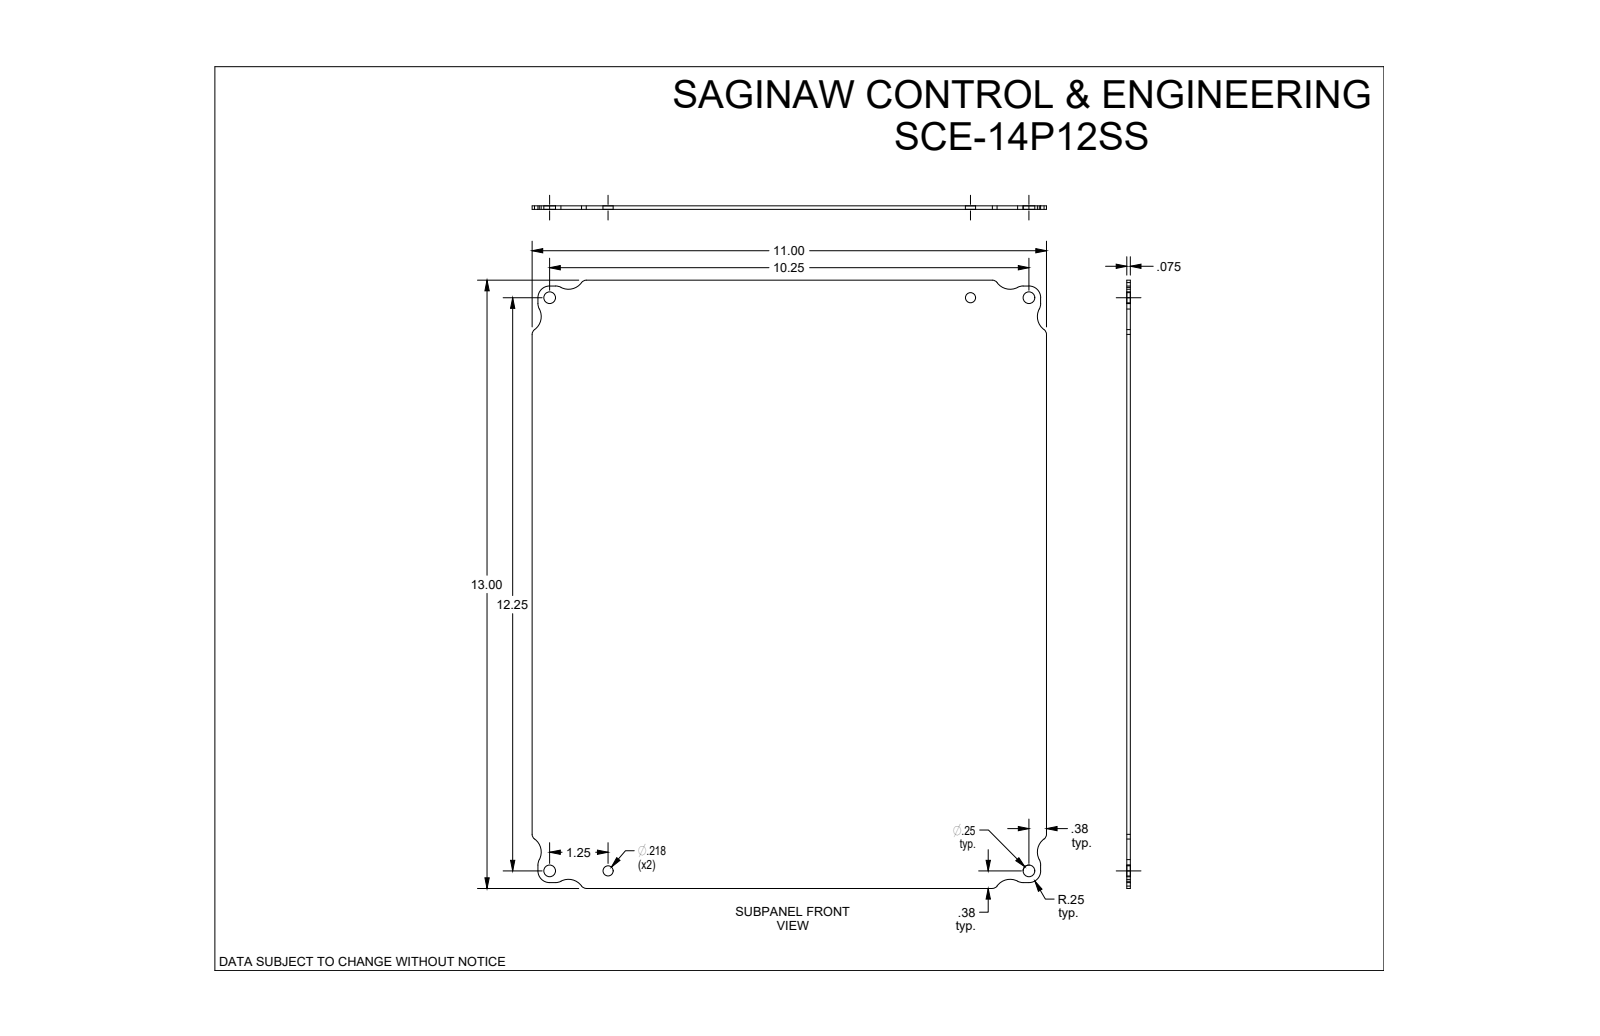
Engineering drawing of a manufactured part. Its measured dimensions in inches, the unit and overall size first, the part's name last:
Units: inches
Overall size (bounding box): 13 × 11 × 0.075
Round holes (diameter × count): ⌀0.25 ×4, ⌀0.218 ×2
Partial cylindrical surfaces — rounded edges, fillets, slot ends (radius × count): R0.25 ×12, R0.125 ×8, R0.344 ×8
Main face-to-face distances: 0.075, 11, 13, 0.125, 10.875, 0.125, 12.875, 10.75, 12.75
Hole centre spacings: 1.25, 9, 10.25, 12.25, 12.313, 15.2, 15.972, 14.495
Volume: 10.61 in³ · Surface area: 286.9 in²
Bodies: 1 solid, 48 faces (14 planar, 34 cylindrical, 0 other)
Part name (STEP PRODUCT): SCE-14P12SS
STEP written by: SolidWorks 2019 (CONFIG_CONTROL_DESIGN)
